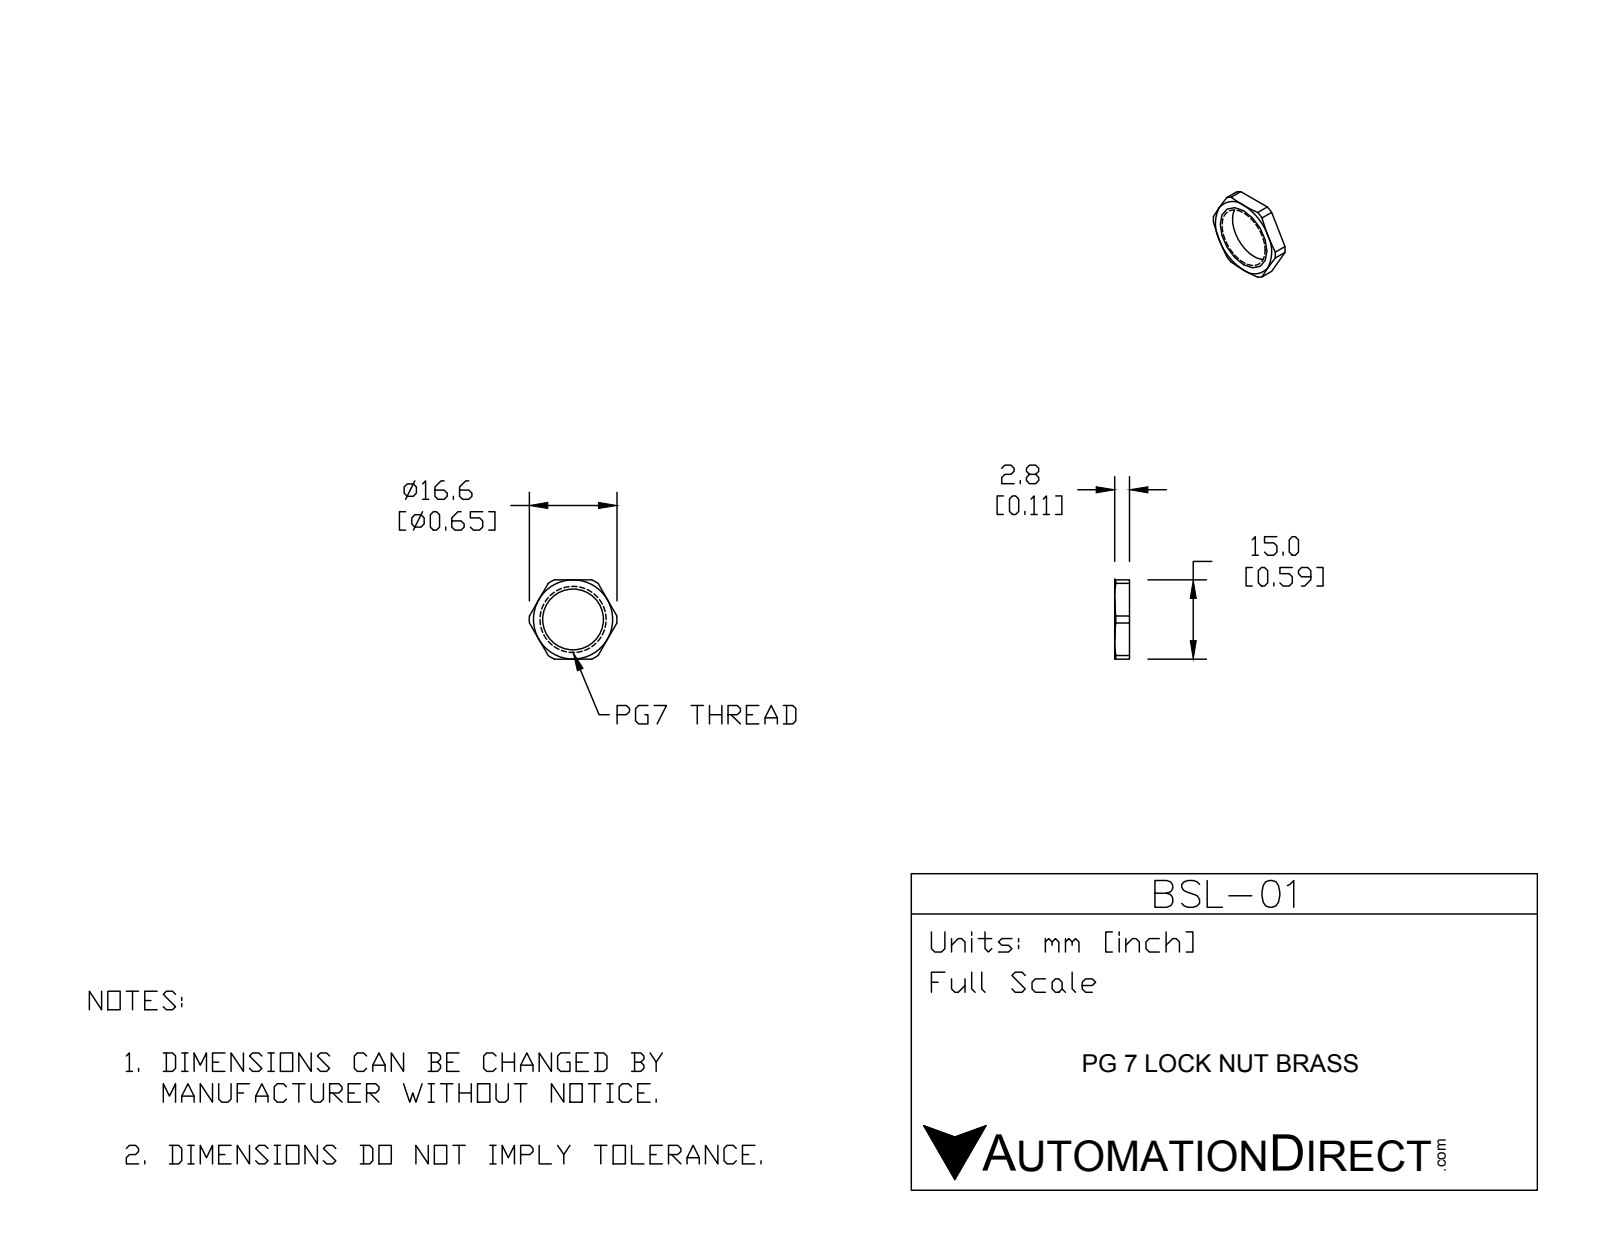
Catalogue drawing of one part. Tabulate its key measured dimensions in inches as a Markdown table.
| quantity | value |
| --- | --- |
| part name | BSL-01 |
| STEP written by | SolidWorks 2015 (CONFIG_CONTROL_DESIGN) |
| units | inches |
| bodies | 1 solid, 23 faces (8 planar, 9 cylindrical, 6 other) |
| overall size | 0.654 × 0.591 × 0.11 |
| volume | 0.015 in³ |
| surface area | 0.648 in² |
| round holes (diameter × count) | 0.453 × 1 |
| partial cylindrical surfaces (radius × count) | 0.327 × 1 |
| main face-to-face distances | 0.11, 0.591 |
